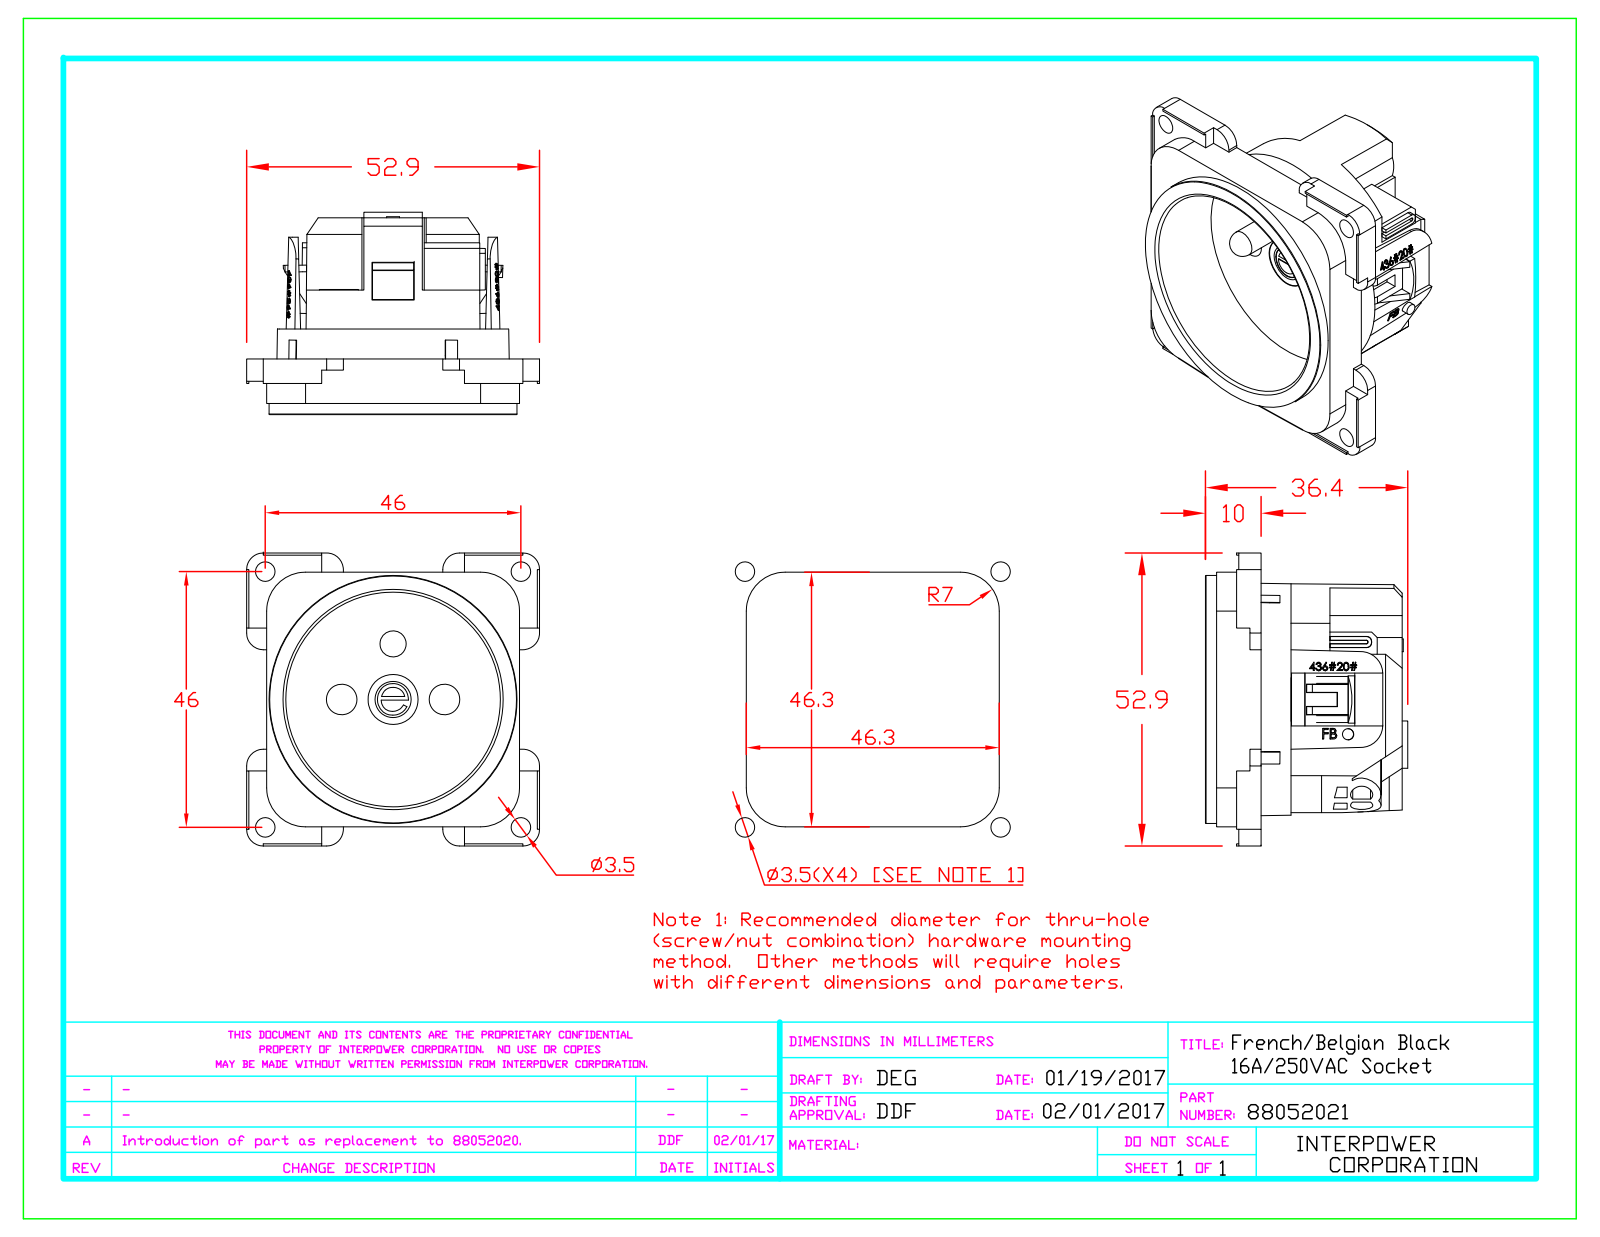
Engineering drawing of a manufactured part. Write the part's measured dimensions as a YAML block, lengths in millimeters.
part_name: "88052021mod"
step_written_by: "Autodesk Inventor 2018 (AUTOMOTIVE_DESIGN)"
units: millimeters
bodies: {solids: 14, faces: 1185, planar: 614, cylindrical: 84, other: 487}
overall_size: [52.7, 52.7, 36.4]
volume: 28084
surface_area: 18622
round_holes:
  - {diameter: 3.5, count: 4}
  - {diameter: 5.5, count: 2}
  - {diameter: 6, count: 2}
  - {diameter: 9, count: 1}
  - {diameter: 38.6, count: 1}
round_bosses_or_shafts:
  - {diameter: 2, count: 2}
  - {diameter: 44.6, count: 1}
  - {diameter: 41.8, count: 1}
  - {diameter: 7, count: 1}
  - {diameter: 6.5, count: 1}
  - {diameter: 5, count: 1}
  - {diameter: 4.7, count: 1}
  - {diameter: 2.3, count: 1}
partial_cylinders:
  - {radius: 3, count: 12}
  - {radius: 2, count: 8}
  - {radius: 0.5, count: 4}
  - {radius: 6, count: 4}
  - {radius: 7, count: 4}
  - {radius: 0.2, count: 2}
  - {radius: 0.9, count: 2}
  - {radius: 1, count: 2}
face_to_face_distances: [1.5, 4, 8, 3.8, 2, 21.6, 6.5, 25.4, 6, 31.9]
hole_center_spacings: [26.67, 32.53, 39.82, 46, 9.5, 18.72, 24, 45.39]
